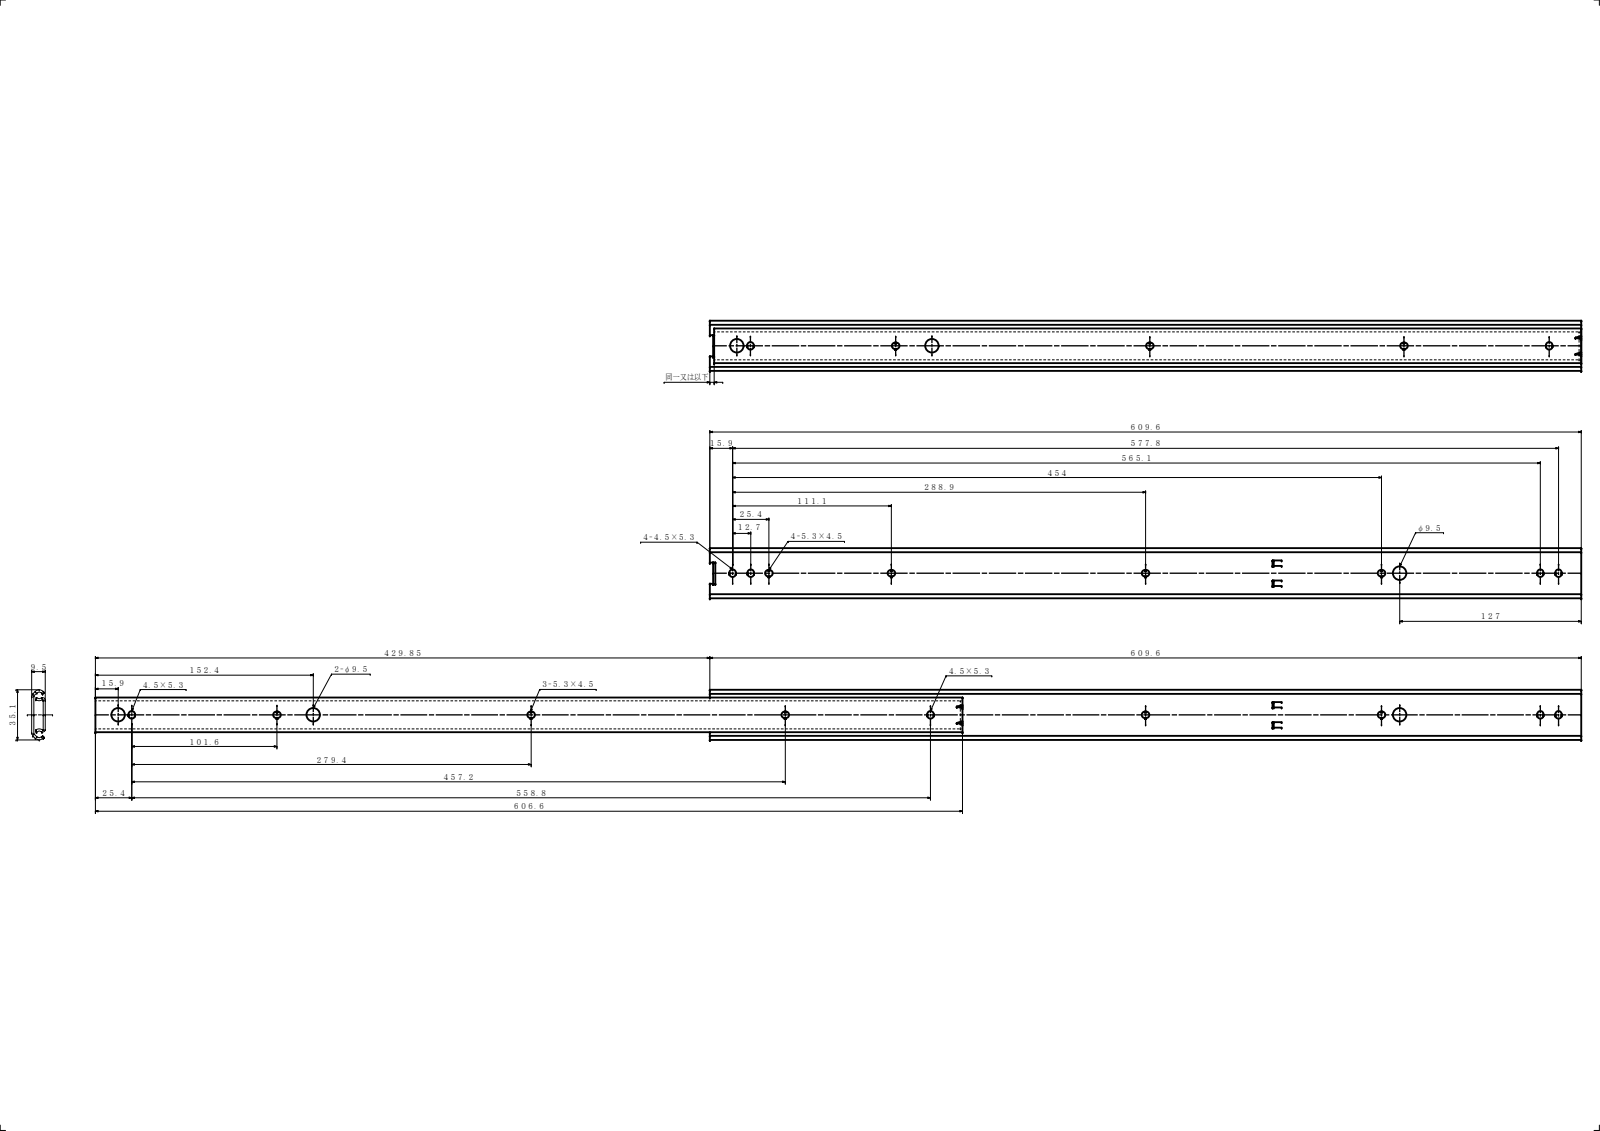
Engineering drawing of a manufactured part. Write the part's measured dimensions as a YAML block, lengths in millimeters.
part_name: "OM U21-24; U21-24; IM U21-24"
step_written_by: "SolidWorks 2019 (CONFIG_CONTROL_DESIGN)"
units: millimeters
bodies: {solids: 2, faces: 143, planar: 70, cylindrical: 73, other: 0}
overall_size: [1039.45, 35.1, 9.5]
volume: 71881
surface_area: 100039
round_holes:
  - {diameter: 9.5, count: 3}
partial_cylinders:
  - {radius: 2.25, count: 26}
  - {radius: 0.4, count: 6}
  - {radius: 1, count: 6}
  - {radius: 3, count: 6}
  - {radius: 2, count: 4}
  - {radius: 0.3, count: 2}
  - {radius: 1.83, count: 2}
  - {radius: 2.38, count: 2}
face_to_face_distances: [1.5, 8, 9.5, 6.5, 25.59, 4.88, 3.38, 24.09, 20.71, 27.09]
hole_center_spacings: [136.5, 760.05, 896.55]
